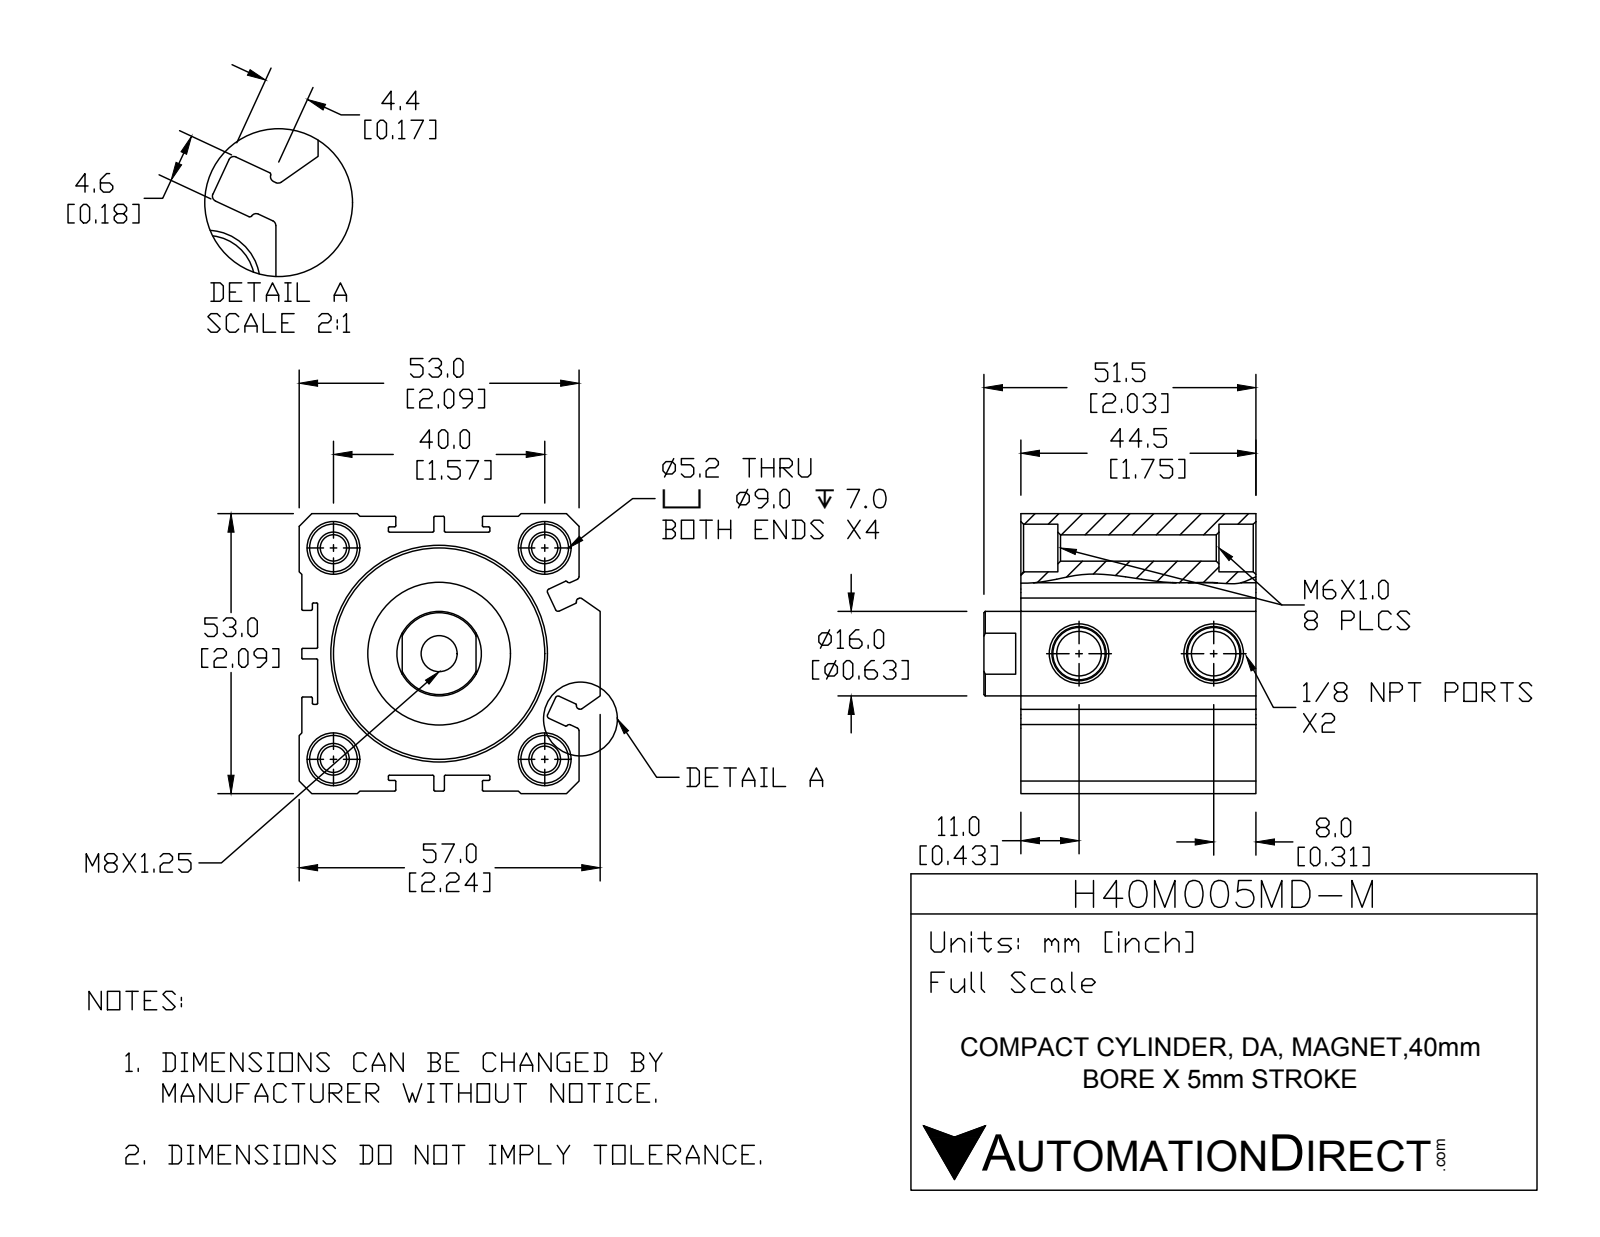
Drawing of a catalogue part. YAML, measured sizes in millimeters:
part_name: "H40M005MD-M-PISTON; H40M005MD-M; H40M005MD-M-BODY"
step_written_by: "SolidWorks 2015 (CONFIG_CONTROL_DESIGN)"
units: millimeters
bodies: {solids: 2, faces: 255, planar: 99, cylindrical: 103, other: 53}
overall_size: [57, 53, 51.5]
volume: 99000
surface_area: 35596
round_holes:
  - {diameter: 5, count: 4}
  - {diameter: 9, count: 4}
  - {diameter: 8.43, count: 2}
  - {diameter: 6.8, count: 1}
  - {diameter: 16, count: 1}
  - {diameter: 29.5, count: 1}
  - {diameter: 40, count: 1}
round_bosses_or_shafts:
  - {diameter: 27, count: 1}
  - {diameter: 25, count: 1}
partial_cylinders:
  - {radius: 0.2, count: 40}
  - {radius: 0.5, count: 12}
face_to_face_distances: [3.5, 49.5, 0.5, 3, 52.5, 53, 49, 44.5, 21.3, 27.95]
hole_center_spacings: [28.28, 40, 56.57, 25.5]
